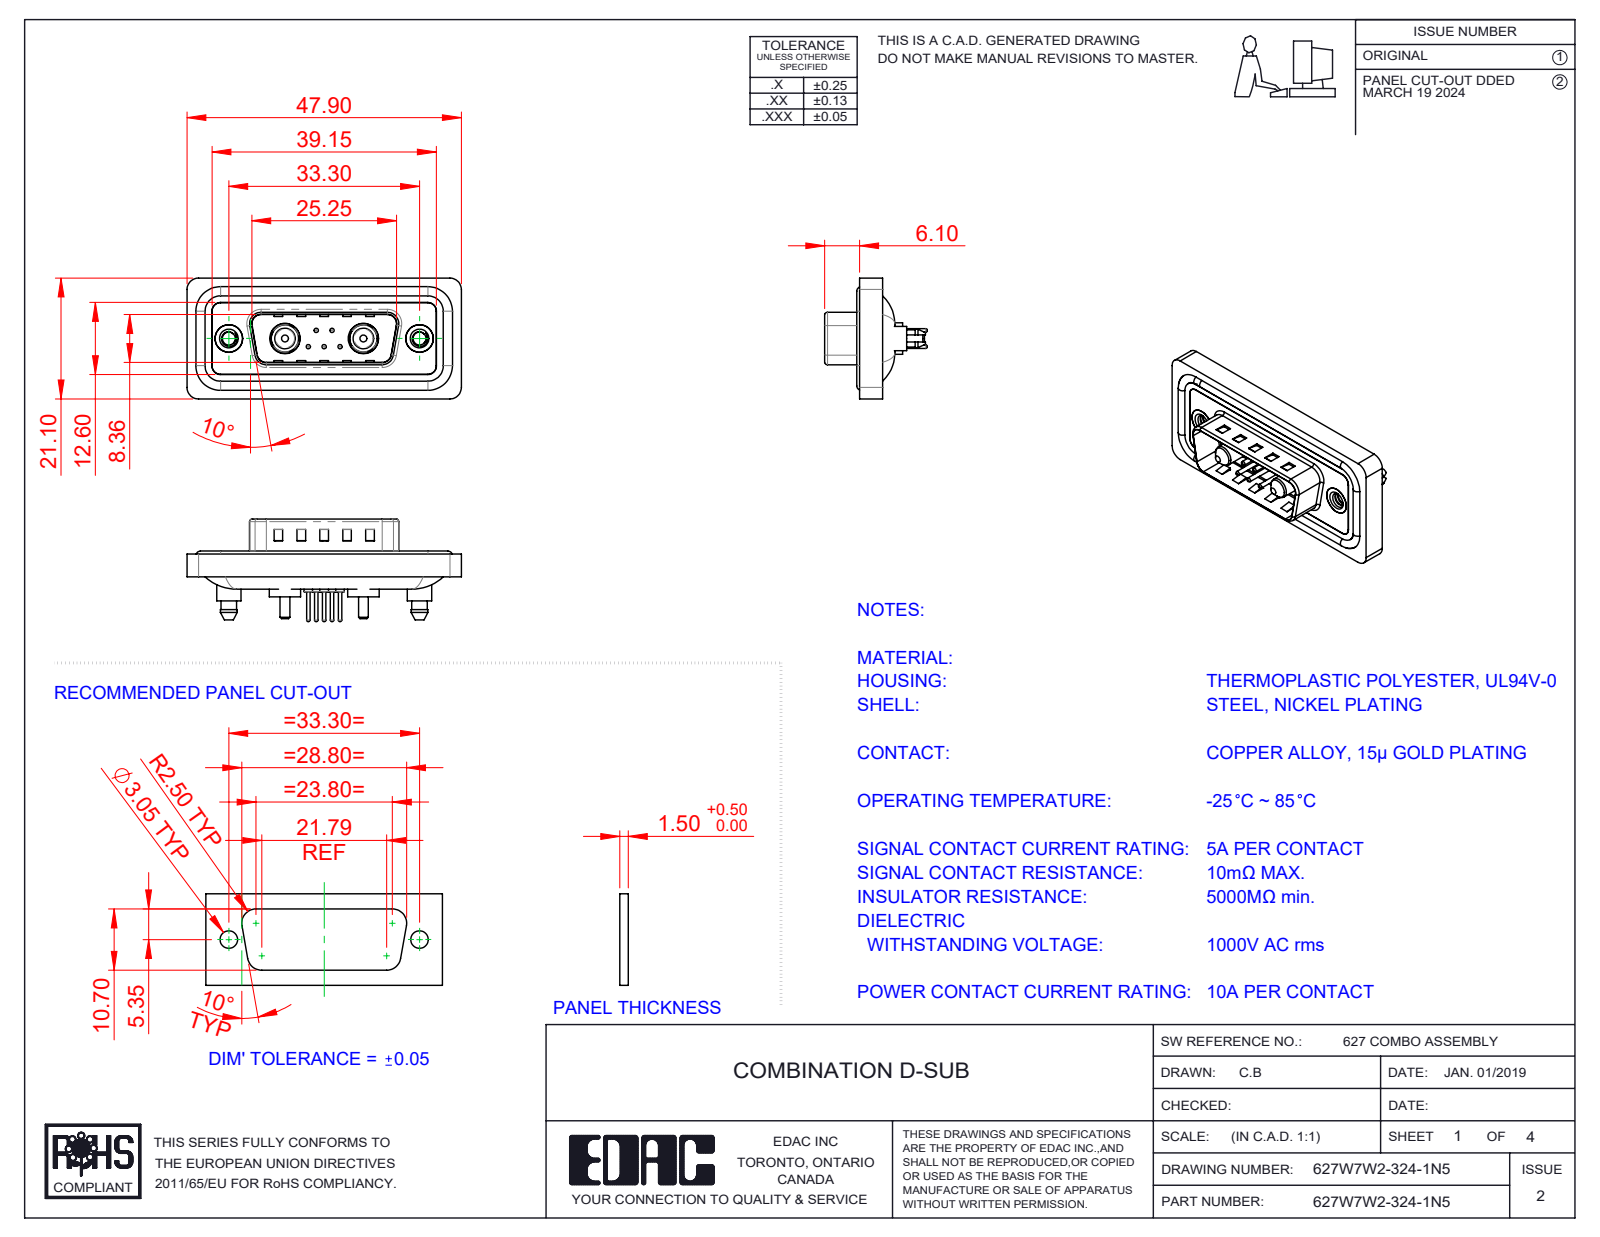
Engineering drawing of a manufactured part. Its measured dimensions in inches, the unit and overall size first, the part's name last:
Units: inches
Overall size (bounding box): 1.886 × 0.831 × 0.705
Round holes (diameter × count): ⌀0.03 ×5, ⌀0.063 ×5, ⌀0.079 ×5, ⌀0.089 ×2, ⌀0.157 ×2, ⌀0.189 ×2, ⌀0.191 ×2, ⌀0.197 ×2, ⌀0.209 ×2
Round bosses / shafts (diameter × count): ⌀0.059 ×5, ⌀0.024 ×5, ⌀0.063 ×4, ⌀0.217 ×2, ⌀0.213 ×2, ⌀0.205 ×2, ⌀0.193 ×2, ⌀0.187 ×2
Partial cylindrical surfaces — rounded edges, fillets, slot ends (radius × count): R0.059 ×28, R0.079 ×20, R0.063 ×10, R0.02 ×8, R0.01 ×4, R0.024 ×4, R0.026 ×4, R0.035 ×4
Main face-to-face distances: 0.016, 0.043, 0.059, 0.063, 0.02, 0.122, 0.114, 0.157, 0.028, 0.032
Hole centre spacings: 0.124, 0.109, 0.386, 0.925, 0.17, 0.17, 0.198, 0.198
Volume: 0.343 in³ · Surface area: 14.11 in²
Bodies: 16 solids, 760 faces (248 planar, 324 cylindrical, 188 other)
Part name (STEP PRODUCT): 627W7W2-324-1N5; Power Pin_10A S; 627Combo Housing_7W2; 627Combo Waterproof Housing_15 Contacts (+5 more)
STEP written by: SolidWorks 2023 (CONFIG_CONTROL_DESIGN)
